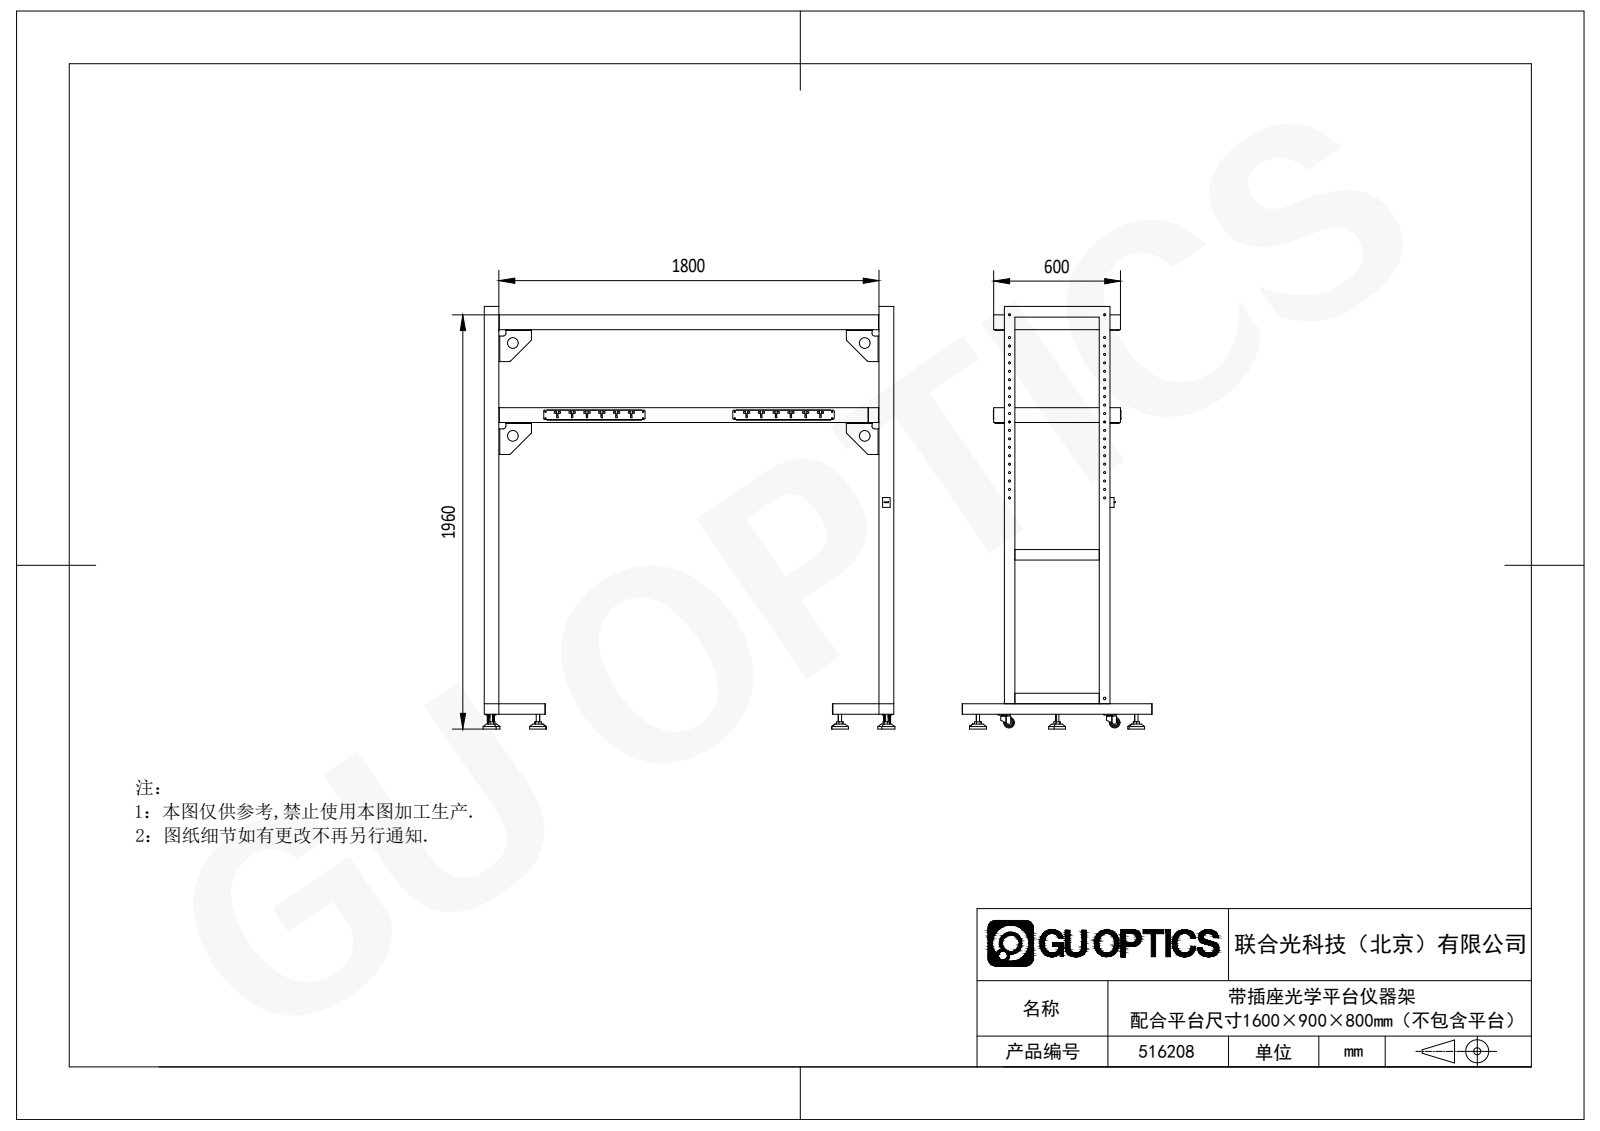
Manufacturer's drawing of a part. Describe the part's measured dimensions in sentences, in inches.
The part is named "516208". Its 3-D file was written by "SolidWorks 2020 (CONFIG_CONTROL_DESIGN)". It is 59 solids with 2531 faces: 1423 planar, 1048 cylindrical and 60 other. Overall it measures 78.78 by 76.772 by 35.433 inches. Its volume is 1 325 cubic inches and its surface area 23 220 square inches. Round holes: 66 of diameter 0.354, 16 of diameter 0.24, 16 of diameter 0.394, 12 of diameter 0.256, 8 of diameter 0.165, 8 of diameter 0.205, 8 of diameter 0.236, 6 of diameter 0.669, 6 of diameter 0.709, 6 of diameter 1.024, 6 of diameter 2.717, 4 of diameter 0.126. Round bosses or shafts: 6 of diameter 3.15, 6 of diameter 0.63, 4 of diameter 1.024, 4 of diameter 0.709, 2 of diameter 1.969, 2 of diameter 0.394. Partial cylindrical surfaces (rounded edges, fillets, slot ends): 36 of radius 0.197, 24 of radius 0.276, 16 of radius 0.118, 12 of radius 0.167, 8 of radius 0.059, 8 of radius 0.158, 4 of radius 0.059, 4 of radius 0.512. The main face-to-face distances are 17.323, 0.059, 0.118, 2.756, 0.079, 1.969, 2.638, 0.098, 17.717, 73.622. The hole center spacings are 1.575, 3.15, 4.724, 6.299, 11.024, 7.874, 9.449, 12.598.
